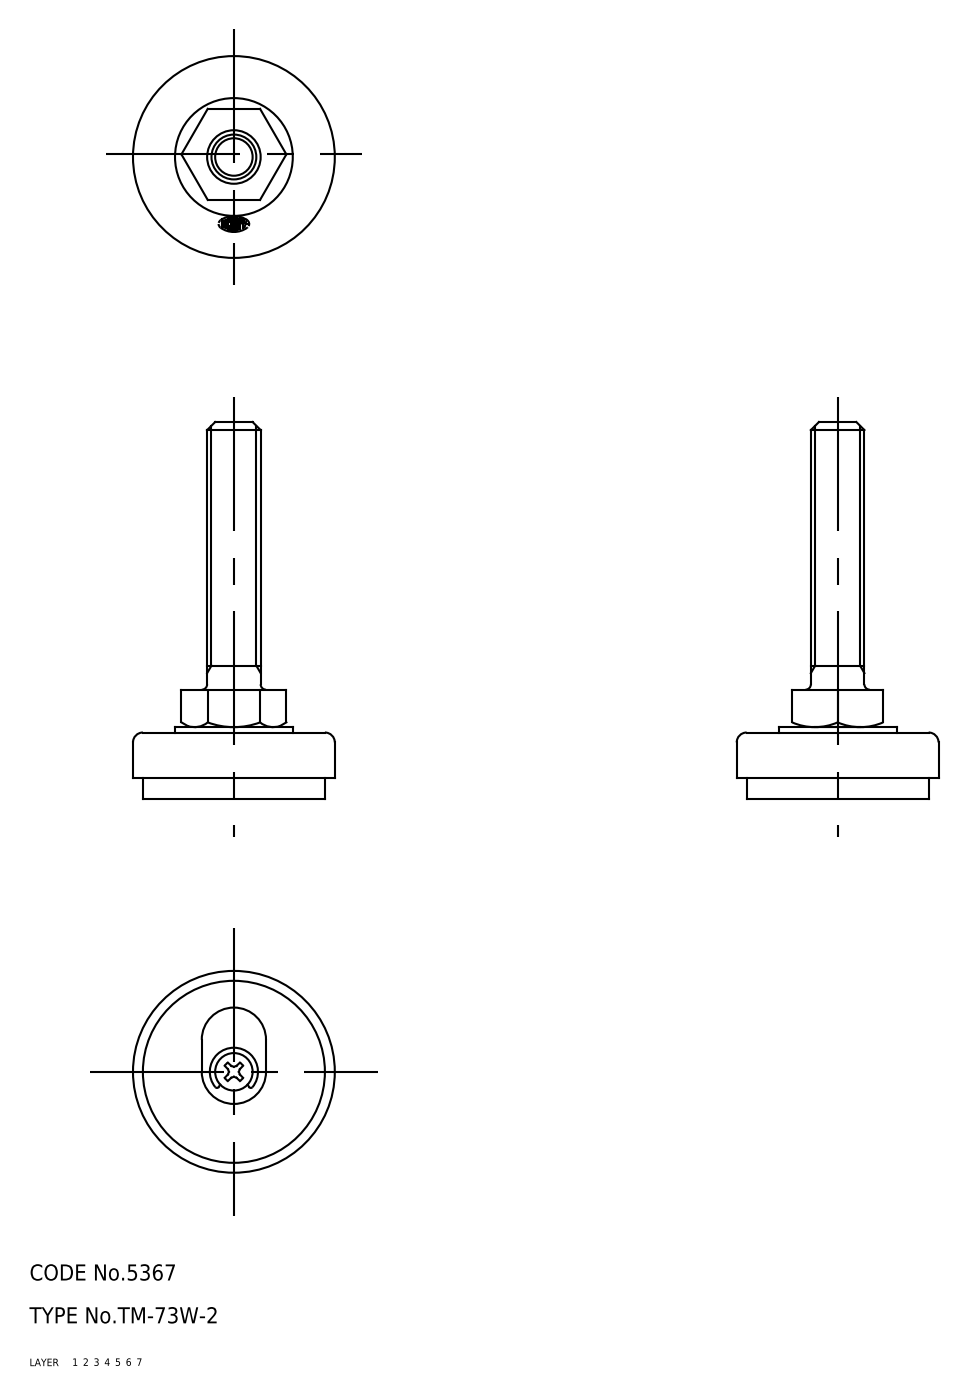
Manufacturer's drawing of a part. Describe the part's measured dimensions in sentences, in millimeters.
The part is named "washer; rubber pad; retainer; cover (+3 more)". Its 3-D file was written by "CADfix (AUTOMOTIVE_DESIGN)". It is 6 solids with 119 faces: 0 planar, 0 cylindrical and 119 other. Overall it measures 70.5 by 37.7 by 37.7 millimeters. Its volume is 17 833 cubic millimeters and its surface area 12 692 square millimeters.
